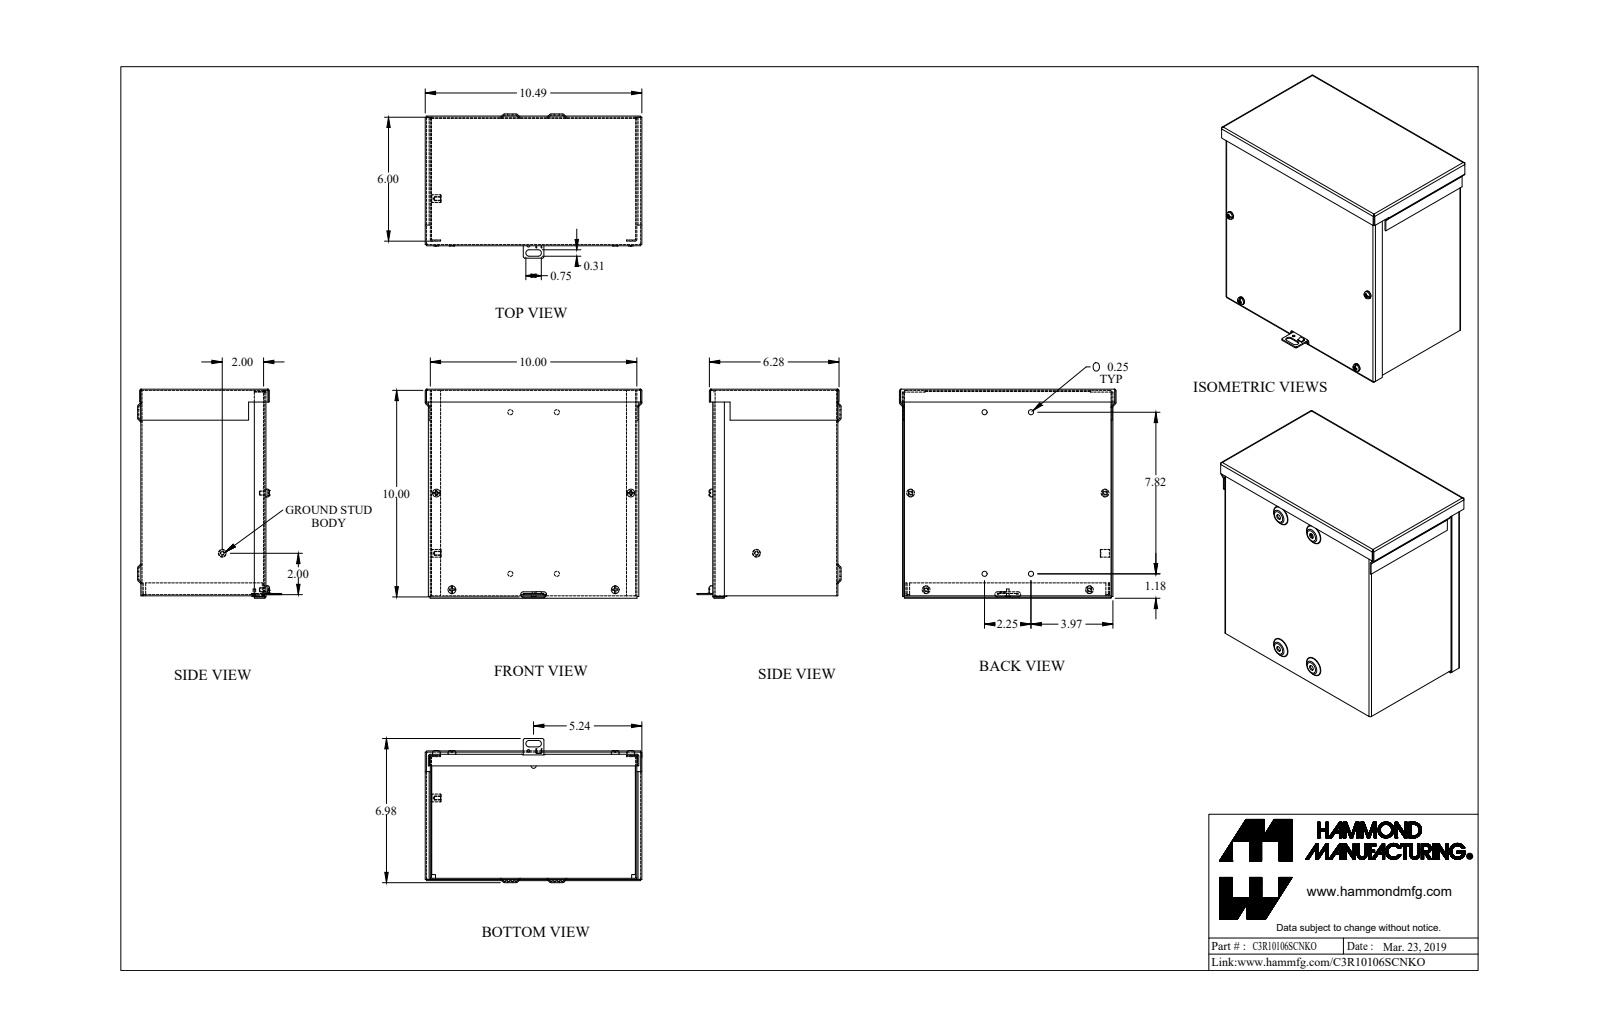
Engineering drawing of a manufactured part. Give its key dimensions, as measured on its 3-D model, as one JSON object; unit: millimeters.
{"part_name": "C3R10106SCNKO_Default", "step_written_by": "SolidWorks 2019 (CONFIG_CONTROL_DESIGN)", "units": "millimeters", "bodies": {"solids": 11, "faces": 404, "planar": 211, "cylindrical": 107, "other": 86}, "overall_size": [266.4, 257, 177.2], "volume_mm3": 481800, "surface_area_mm2": 672300, "round_holes": [[4.3, 4], [6.4, 4], [3.2, 1], [3.5, 1], [4, 1]], "round_bosses_or_shafts": [[9.5, 4], [4.8, 4], [9.5, 1], [3.2, 1]], "partial_cylinders_radius": [[0.7, 21], [2.2, 21], [2.8, 8], [3.2, 8], [4, 2]], "face_to_face_distances": [1.4, 152.4, 252.6, 254, 151, 153.8, 1.4, 251.1, 251.1, 252.6], "hole_center_spacings": [134.7, 178.3, 57.2, 74.4, 120.4, 130.5, 198.6, 206.6]}
